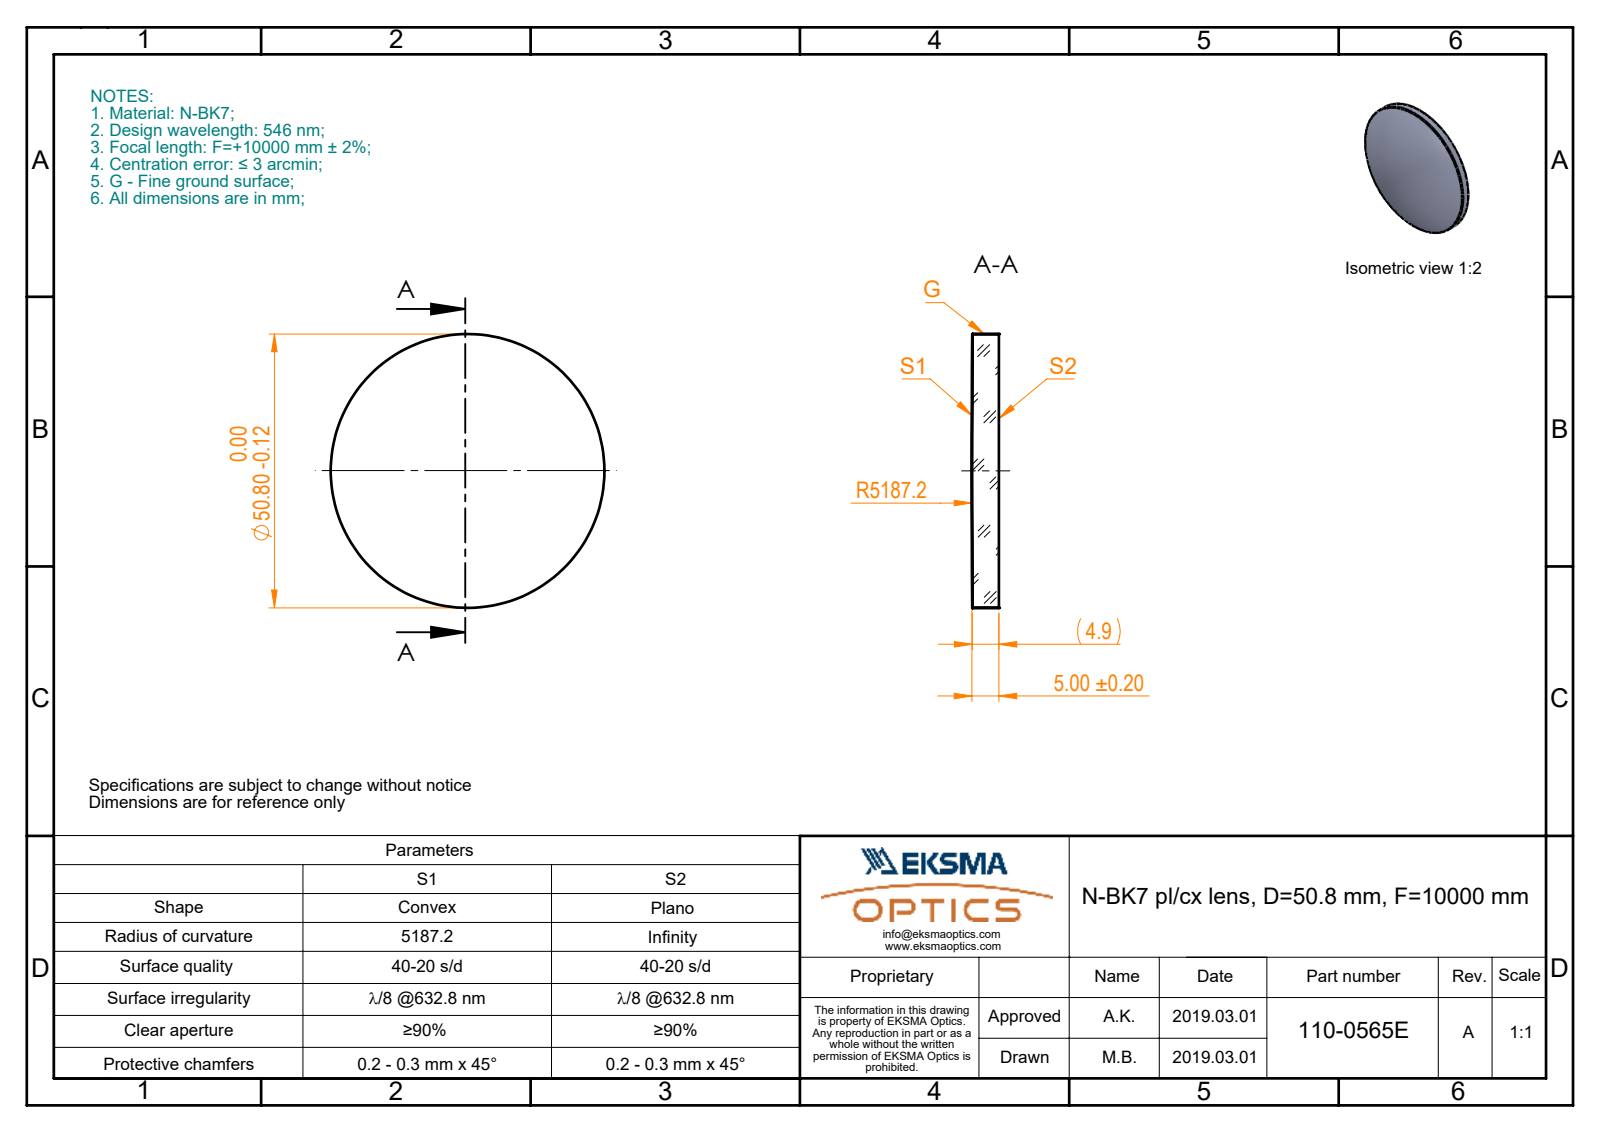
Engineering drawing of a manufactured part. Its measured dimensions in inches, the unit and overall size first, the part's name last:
Units: inches
Overall size (bounding box): 2 × 2 × 0.197
Round bosses / shafts (diameter × count): ⌀2 ×1
Volume: 0.615 in³ · Surface area: 7.505 in²
Bodies: 1 solid, 5 faces (1 planar, 2 cylindrical, 2 other)
Part name (STEP PRODUCT): 110-0565E BK7 pl-cx 50.8 F10000
STEP written by: SolidWorks 2017 (CONFIG_CONTROL_DESIGN)
